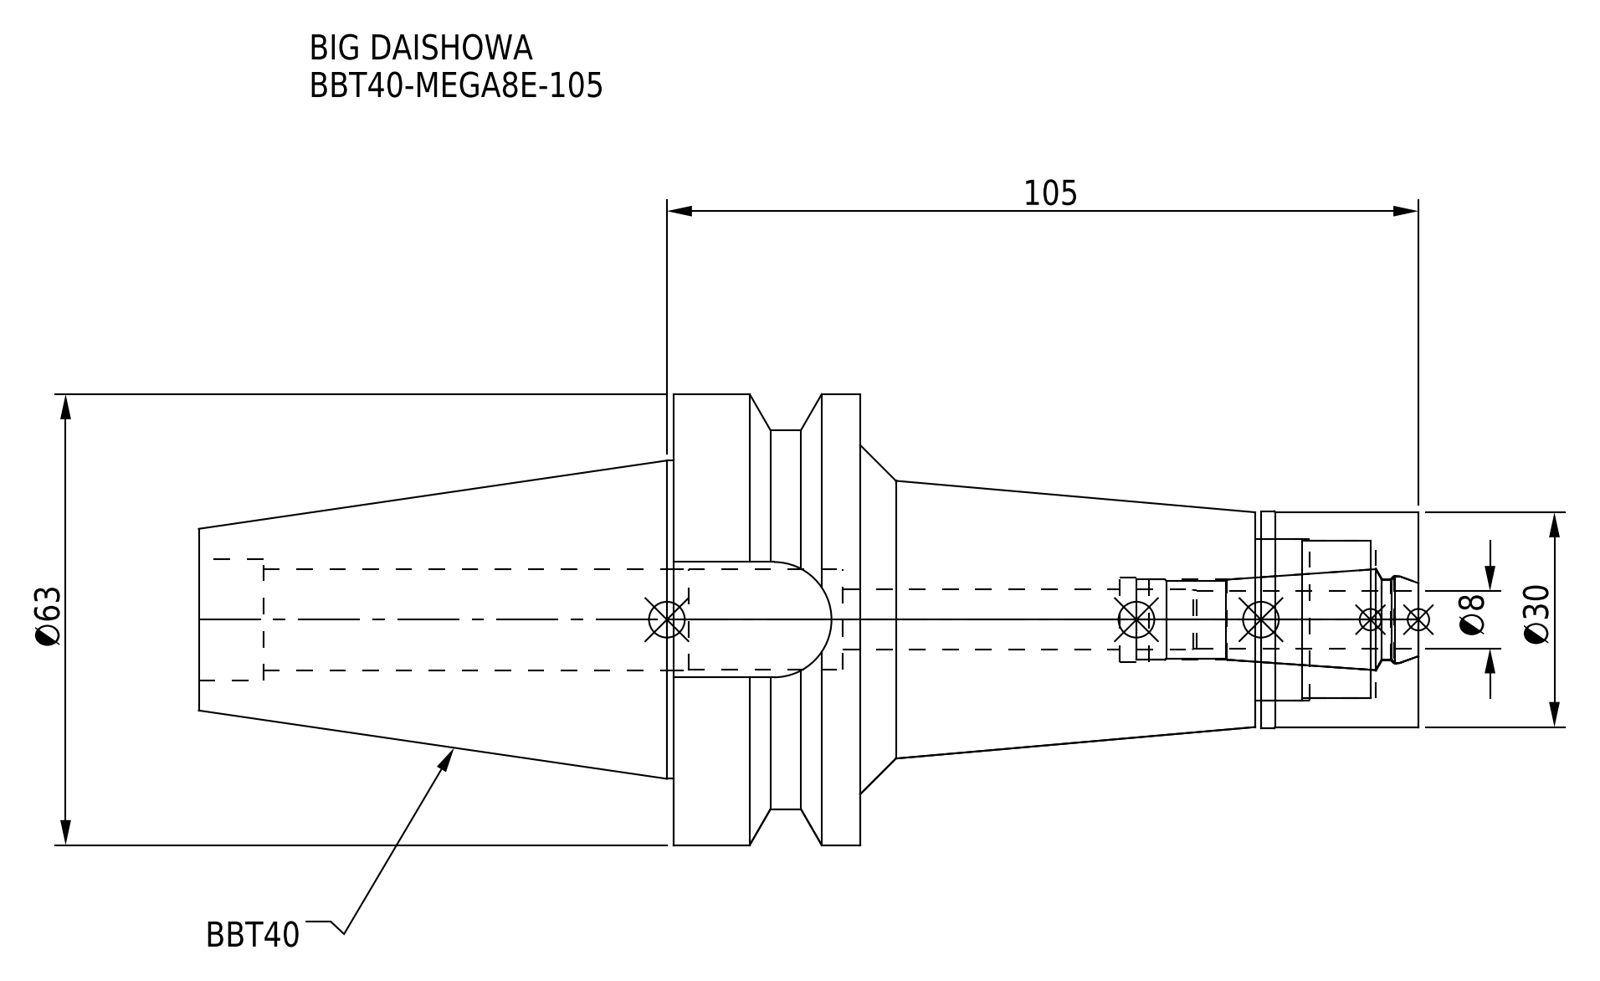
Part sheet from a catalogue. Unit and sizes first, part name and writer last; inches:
Units: inches
Overall size (bounding box): 6.709 × 2.48 × 2.48
Round holes (diameter × count): ⌀0.331 ×1, ⌀0.441 ×1, ⌀0.449 ×1, ⌀0.465 ×1, ⌀0.484 ×1, ⌀0.551 ×1, ⌀0.559 ×1, ⌀0.669 ×1, ⌀0.866 ×1, ⌀0.886 ×1
Round bosses / shafts (diameter × count): ⌀2.48 ×1, ⌀2.087 ×1, ⌀1.75 ×1, ⌀1.193 ×1, ⌀1.181 ×1
Partial cylindrical surfaces — rounded edges, fillets, slot ends (radius × count): R0.317 ×1
Main face-to-face distances: 1.024, 3.071, 4.094, 0.634, 1.772, 0.866, 2.205, 3.228, 0.898, 0.031
Volume: 11.23 in³ · Surface area: 55.99 in²
Bodies: 2 solids, 81 faces (21 planar, 40 cylindrical, 20 other)
Part name (STEP PRODUCT): BBT40-MEGA8E-105-080.stp; DXF_TEMP_ASSY_ASM_4_ASM.stp; BBT40ME08105-080_ASM.stp; BBT40-MEGA8E-105-080-FreeParts (+3 more)
STEP written by: SolidWorks 2019 (CONFIG_CONTROL_DESIGN)
